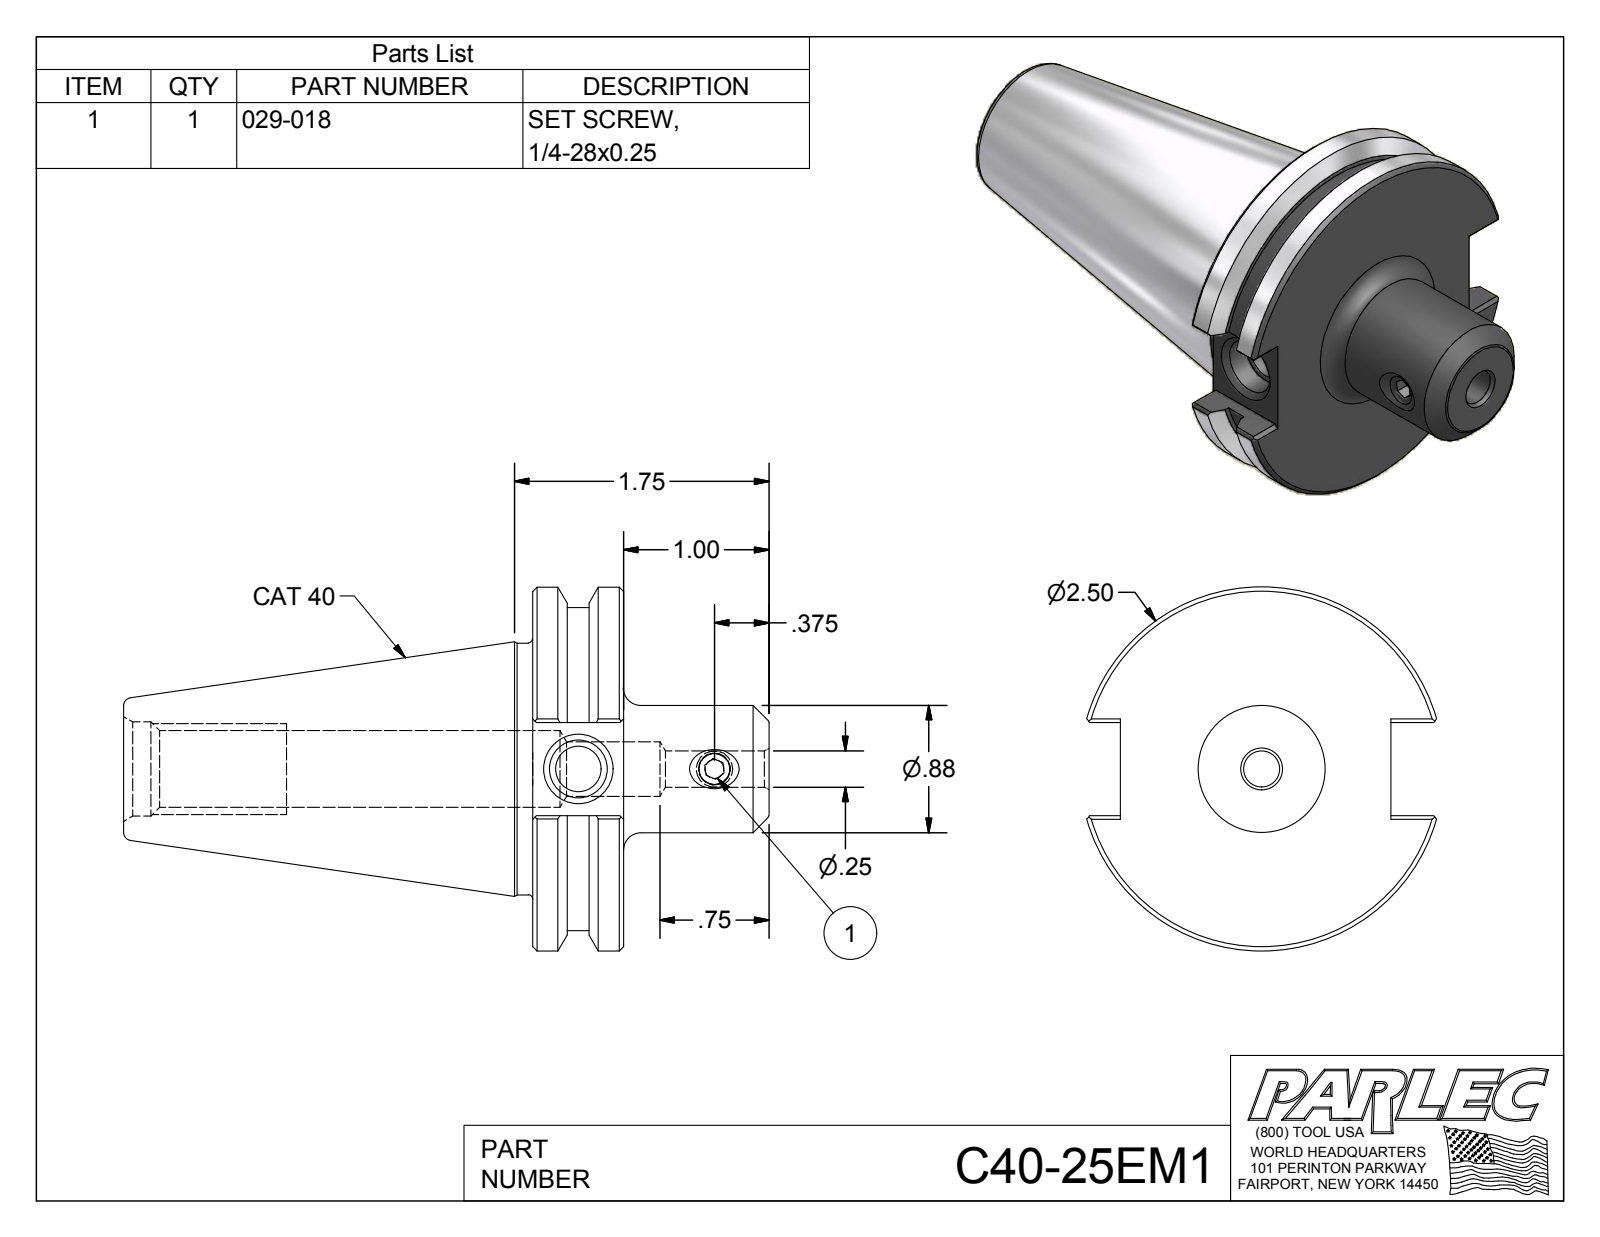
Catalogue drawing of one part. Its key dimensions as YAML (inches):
part_name: "C40-25EM1; C40-25EM1-1; 029-018"
step_written_by: "Autodesk Inventor 2012 (AUTOMOTIVE_DESIGN)"
units: inches
bodies: {solids: 2, faces: 81, planar: 40, cylindrical: 16, other: 25}
overall_size: [4.438, 2.5, 2.403]
volume: 6.695
surface_area: 35.12
round_holes:
  - {diameter: 0.211, count: 1}
  - {diameter: 0.25, count: 1}
  - {diameter: 0.315, count: 1}
  - {diameter: 0.375, count: 1}
  - {diameter: 0.396, count: 1}
  - {diameter: 0.527, count: 1}
  - {diameter: 0.648, count: 1}
round_bosses_or_shafts:
  - {diameter: 2.5, count: 1}
  - {diameter: 2.219, count: 1}
  - {diameter: 1.73, count: 1}
  - {diameter: 0.875, count: 1}
  - {diameter: 0.25, count: 1}
face_to_face_distances: [0.625, 1.625, 1, 0.64, 1.86, 2.813, 3.437, 4.437, 3.201, 0.389]
hole_center_spacings: [0.935]
